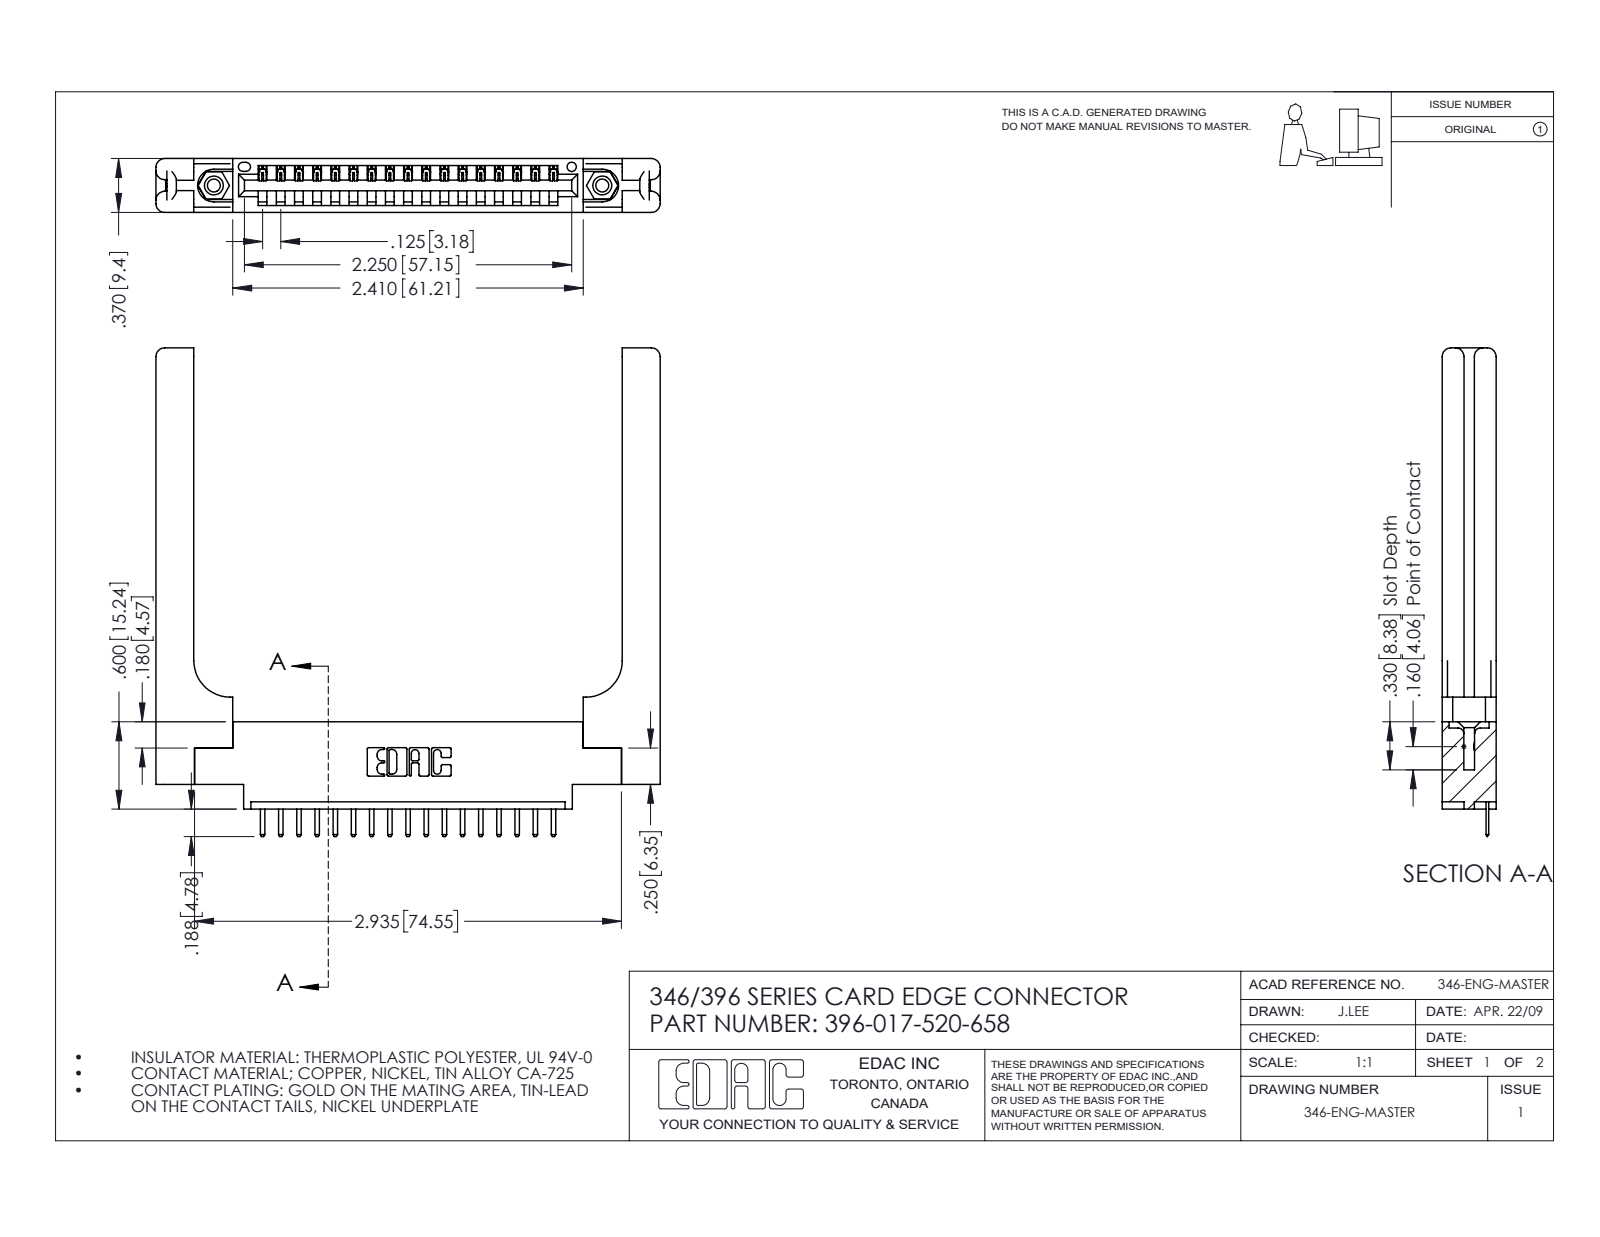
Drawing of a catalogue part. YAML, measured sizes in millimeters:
part_name: "345-292-001_345-293-120; 346 Part_0.170 Offset - 0.156 Dia-TH; 396-017-520-658; 346-220-058_345-220-058 (+1 more)"
step_written_by: "SolidWorks 2016 (CONFIG_CONTROL_DESIGN)"
units: millimeters
bodies: {solids: 22, faces: 1436, planar: 942, cylindrical: 434, other: 60}
overall_size: [88, 85.3, 9.4]
volume: 15600
surface_area: 14960
round_holes:
  - {diameter: 2.3, count: 2}
  - {diameter: 3.2, count: 2}
  - {diameter: 4, count: 2}
  - {diameter: 1.6, count: 1}
round_bosses_or_shafts:
  - {diameter: 3.9, count: 2}
partial_cylinders:
  - {radius: 0.3, count: 36}
  - {radius: 0.2, count: 34}
  - {radius: 0.3, count: 22}
  - {radius: 1.5, count: 16}
  - {radius: 0.2, count: 6}
  - {radius: 0.8, count: 6}
  - {radius: 0.7, count: 3}
  - {radius: 0.8, count: 2}
face_to_face_distances: [9.4, 3.8, 1.8, 3.8, 1.2, 8.2, 6.4, 2.6, 5.6, 4.4]
hole_center_spacings: [6.2, 62.6, 67.8]
